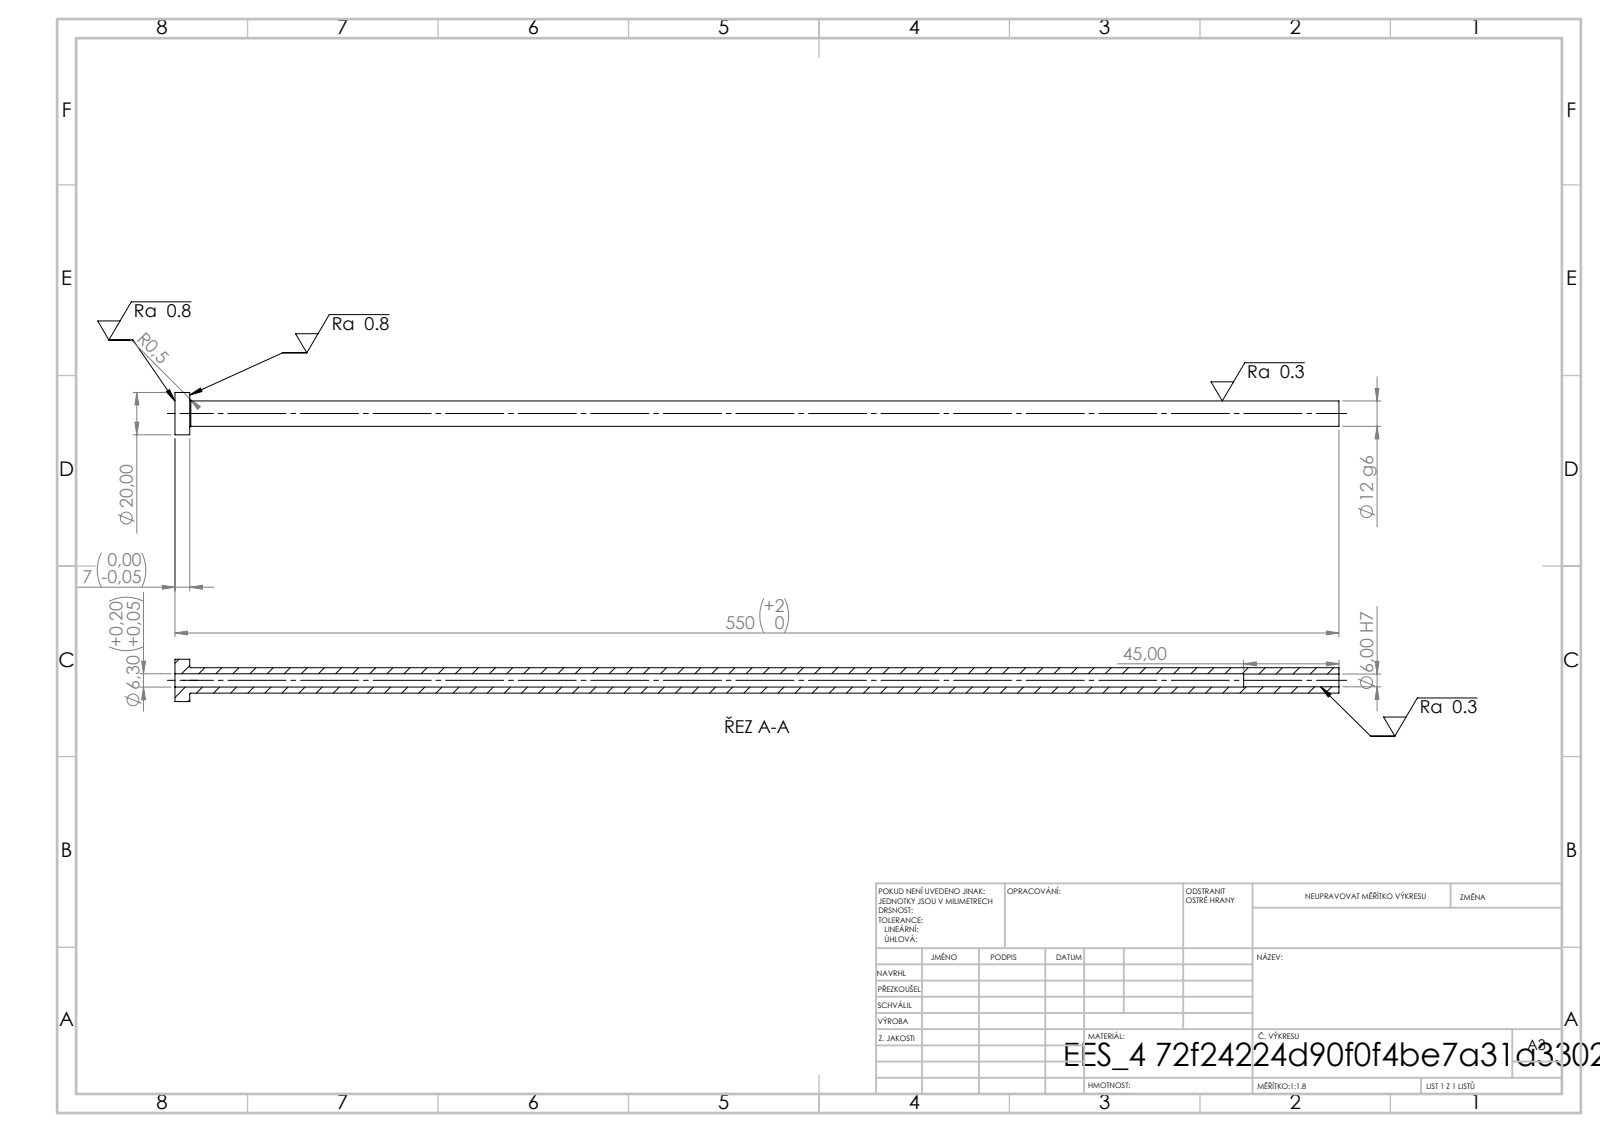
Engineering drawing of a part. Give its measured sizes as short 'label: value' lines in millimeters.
written by: SolidWorks 2019 (CONFIG_CONTROL_DESIGN)
unit: mm
bodies: 1 solid, 14 faces (4 planar, 8 cylindrical, 2 other)
size: 550 × 20 × 20
volume: 46 599 mm³; area: 32 317 mm²
holes: 1× ⌀6, 1× ⌀6.3
bosses: 1× ⌀20, 1× ⌀12
face distances: 7, 550, 543, 505, 498, 45
